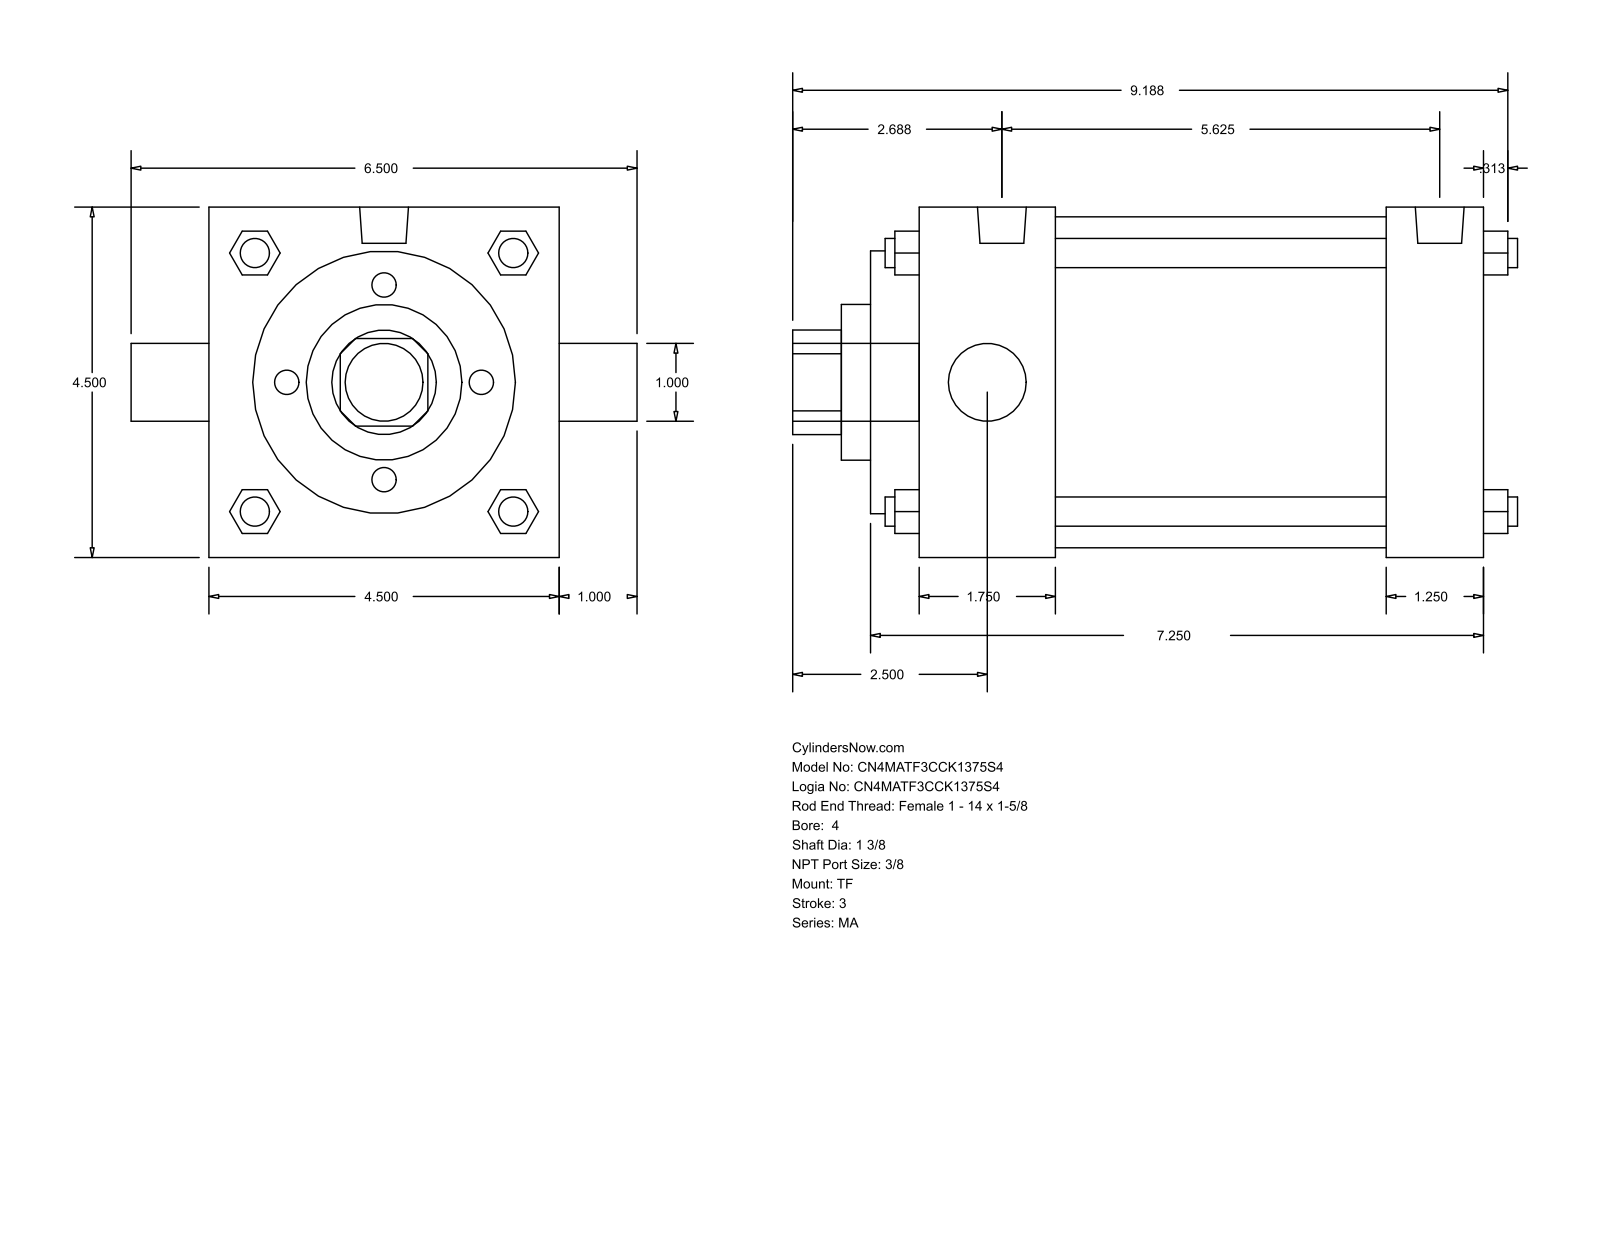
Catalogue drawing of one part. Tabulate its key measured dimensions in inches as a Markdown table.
| quantity | value |
| --- | --- |
| part name | MA_TF__0400_1.375 |
| STEP written by | GSSL Pune (CONFIG_CONTROL_DESIGN) |
| units | inches |
| bodies | 0 solids, 122 faces (93 planar, 29 cylindrical, 0 other) |
| overall size | 9.313 × 6.5 × 4.5 |
| round holes (diameter × count) | 1 × 1, 1.375 × 1, 2 × 1, 3.375 × 1, 4.25 × 1 |
| round bosses / shafts (diameter × count) | 0.375 × 4, 0.437 × 3, 0.627 × 2, 1 × 1 |
| partial cylindrical surfaces (radius × count) | 0.672 × 1 |
| main face-to-face distances | 4.5, 7.25, 0.625, 7.875, 6.625, 6, 1.25, 2.375, 1.75, 4.25 |
